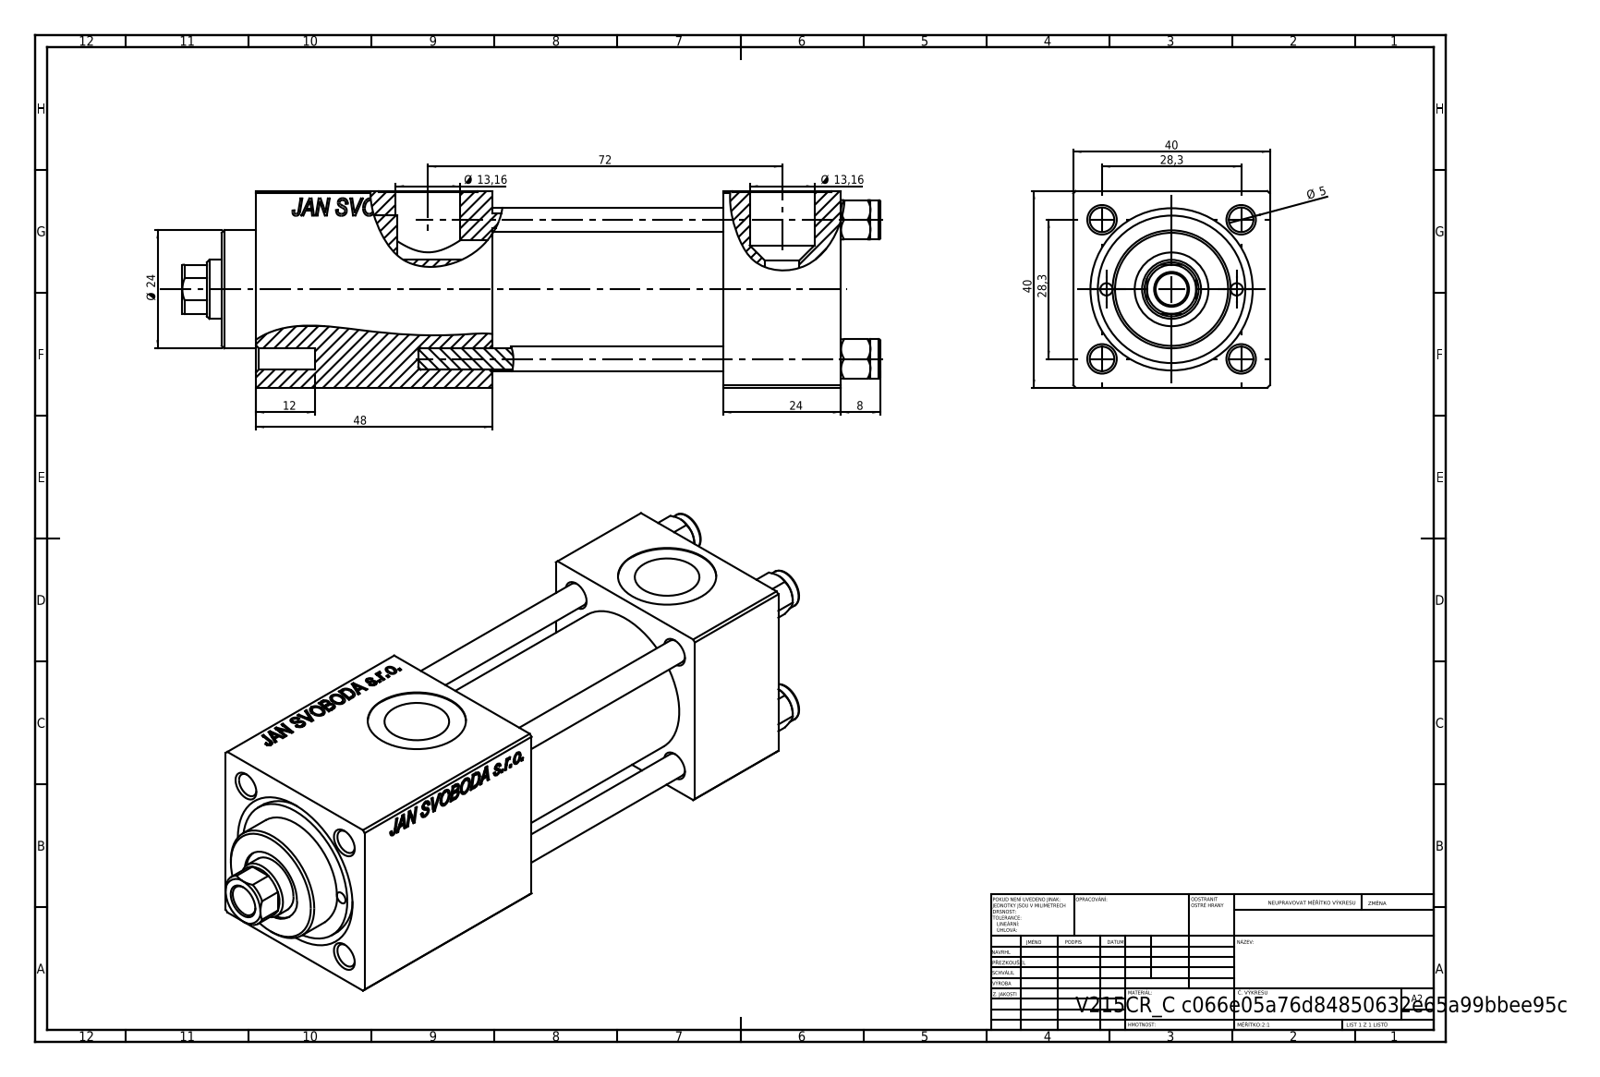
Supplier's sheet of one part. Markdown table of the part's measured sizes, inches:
| quantity | value |
| --- | --- |
| part name | V215_VC_A; NUT_M5_C; V215CR_C_TYCINKA; V215CR_C_Body (+1 more) |
| STEP written by | SolidWorks 2019 (CONFIG_CONTROL_DESIGN) |
| units | inches |
| bodies | 11 solids, 1154 faces (527 planar, 91 cylindrical, 536 other) |
| overall size | 5.591 × 1.575 × 1.575 |
| volume | 8.681 in³ |
| surface area | 84.51 in² |
| round holes (diameter × count) | 0.197 × 4, 0.787 × 3, 0.098 × 2, 0.276 × 2, 0.518 × 2, 0.256 × 1, 0.472 × 1, 0.591 × 1, 0.984 × 1, 1.181 × 1 |
| round bosses / shafts (diameter × count) | 0.315 × 4, 1.22 × 1, 0.945 × 1 |
| partial cylindrical surfaces (radius × count) | 0.217 × 1 |
| main face-to-face distances | 1.575, 0.945, 3.555, 2.61, 1.89, 2.795, 1.85, 0.76, 4.685, 3.74 |
| hole center spacings | 0.558, 0.788, 1.114, 1.214, 0.522, 1.576, 1.043, 2.835 |
